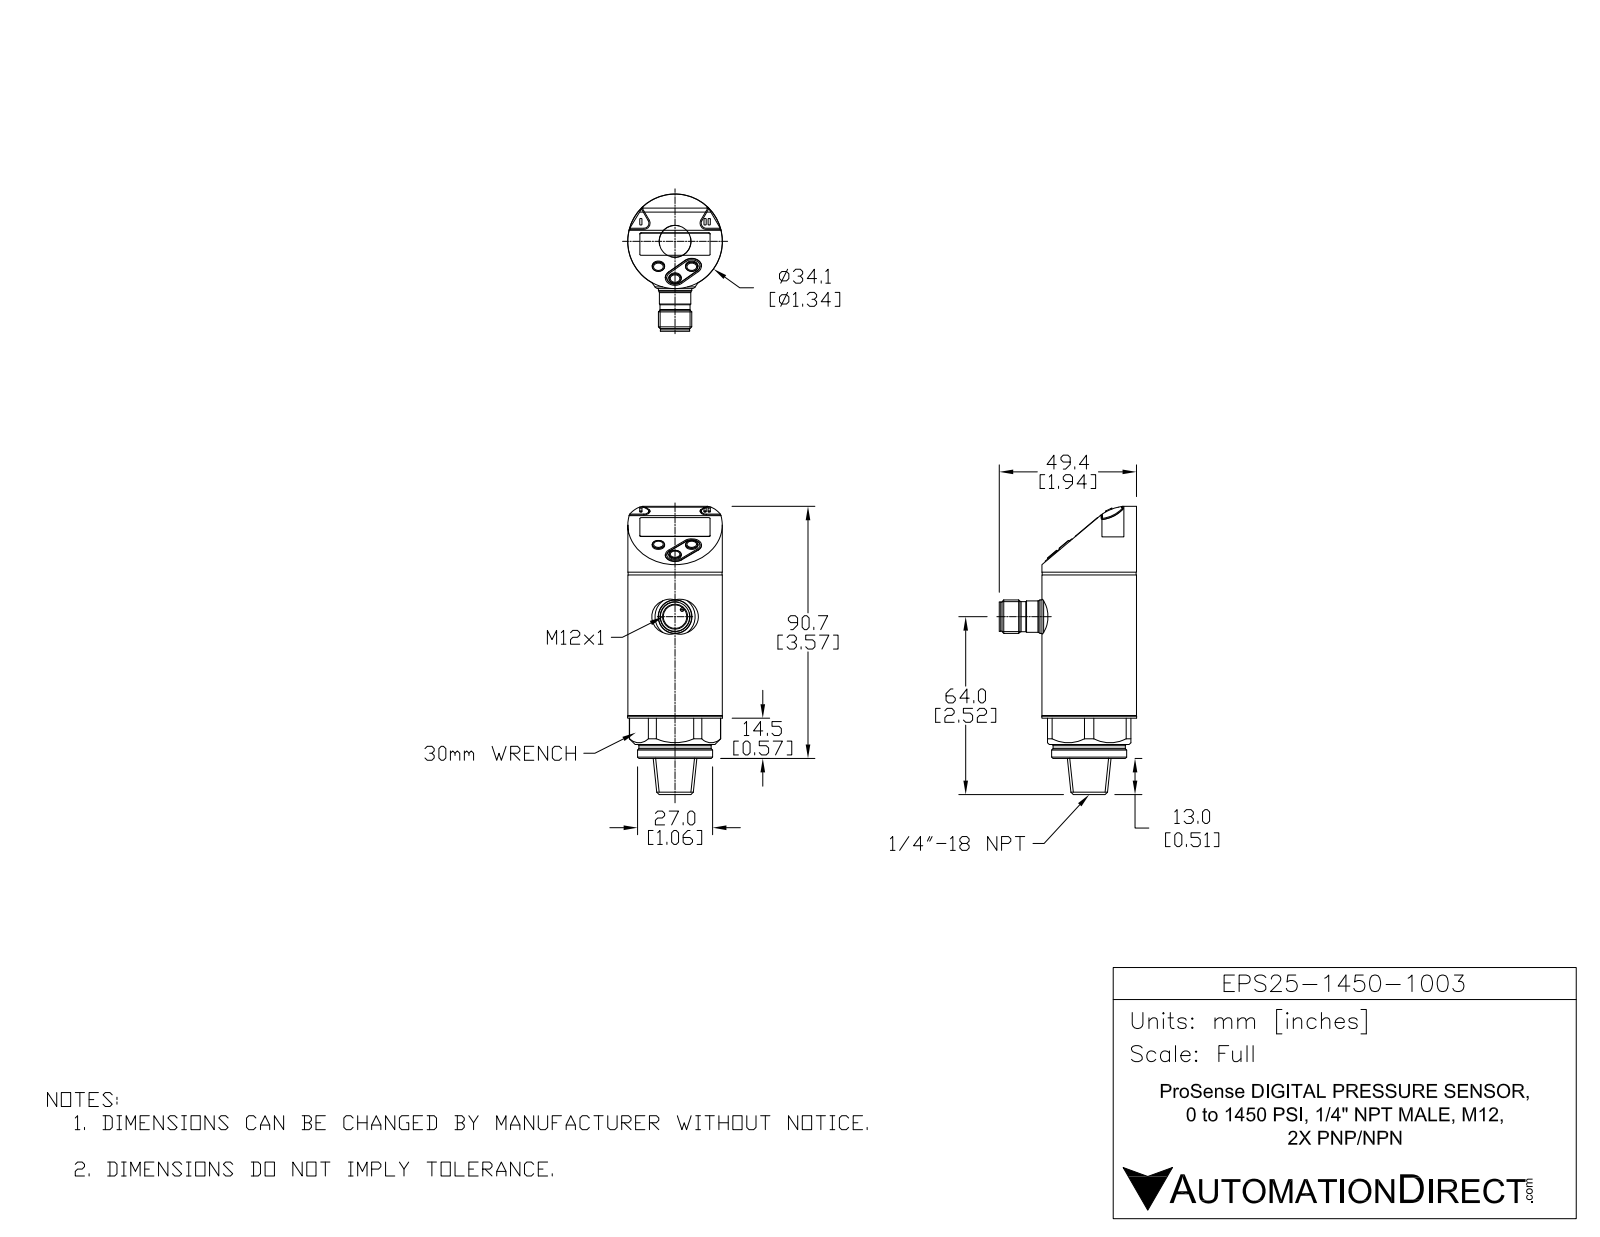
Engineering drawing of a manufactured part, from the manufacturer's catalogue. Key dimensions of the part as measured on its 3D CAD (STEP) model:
Part name (STEP PRODUCT): EPS25-360-1003
STEP written by: SolidWorks 2016 (AUTOMOTIVE_DESIGN)
Units: millimetres
Bodies: 11 solids, 370 faces (207 planar, 84 cylindrical, 79 other)
Overall size (bounding box): 103.7 × 49.4 × 34.1
Volume: 72 203 mm³ · Surface area: 21 365 mm²
Round holes (diameter × count): ⌀4.2 ×1, ⌀8.45 ×1
Round bosses / shafts (diameter × count): ⌀1.4 ×4, ⌀1 ×4, ⌀34.1 ×1, ⌀34 ×1, ⌀33.8 ×1, ⌀27 ×1, ⌀26 ×1, ⌀12 ×1
Partial cylindrical surfaces — rounded edges, fillets, slot ends (radius × count): R1.8 ×2, R2.2 ×2, R3 ×2, R3.5 ×2, R15 ×2, R0.61 ×1, R6.8 ×1, R16.44 ×1
Main face-to-face distances: 0.68, 11.5, 12.18, 10.68, 1.5, 10, 2, 2.5, 14, 4
